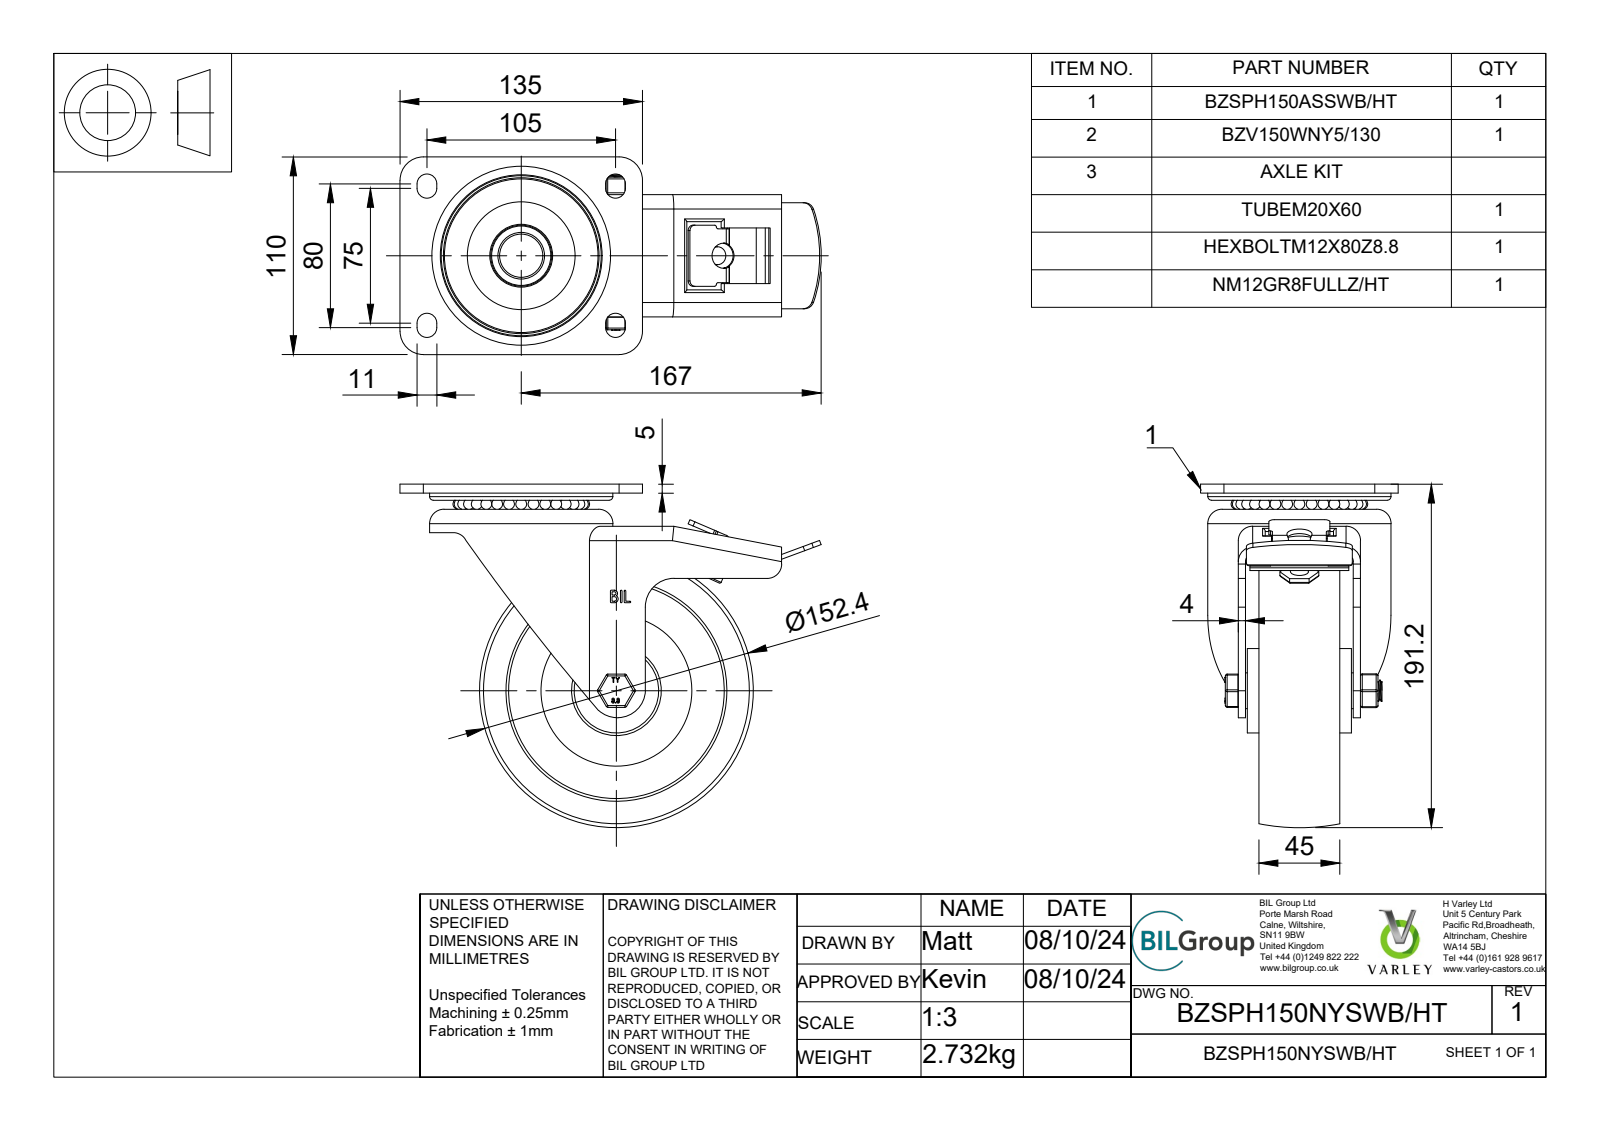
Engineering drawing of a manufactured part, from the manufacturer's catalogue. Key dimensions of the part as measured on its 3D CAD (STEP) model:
Part name (STEP PRODUCT): BZSPH150NYSWB/HT v3; BZSPH150ASSWB/HT - 60 v1; ZINC PLATED, PRESSED STEEL TOP PLATE; ZINC PLATED, PRESSED STEEL TOP PLATE Geometry (+6 more)
STEP written by: Autodesk Translation Framework v13.20.0.188 (AUTOMOTIVE_DESIGN)
Units: millimetres
Bodies: 126 solids, 722 faces (265 planar, 199 cylindrical, 258 other)
Overall size (bounding box): 234.5 × 191.2 × 110
Volume: 744 185 mm³ · Surface area: 234 787 mm²
Round holes (diameter × count): ⌀10 ×2, ⌀12 ×1, ⌀12.2 ×1, ⌀12.5 ×1, ⌀14 ×1, ⌀20.5 ×1, ⌀94 ×1
Round bosses / shafts (diameter × count): ⌀102 ×1, ⌀74 ×1, ⌀47 ×1, ⌀36 ×1, ⌀33 ×1, ⌀26 ×1, ⌀24 ×1, ⌀19.9 ×1
Partial cylindrical surfaces — rounded edges, fillets, slot ends (radius × count): R1 ×40, R1.5 ×10, R5.5 ×10, R4 ×7, R0.75 ×6, R2 ×6, R8 ×6, R3 ×4
Main face-to-face distances: 4, 9, 5, 17, 28, 1, 7.5, 56.5, 39.5, 52.5
